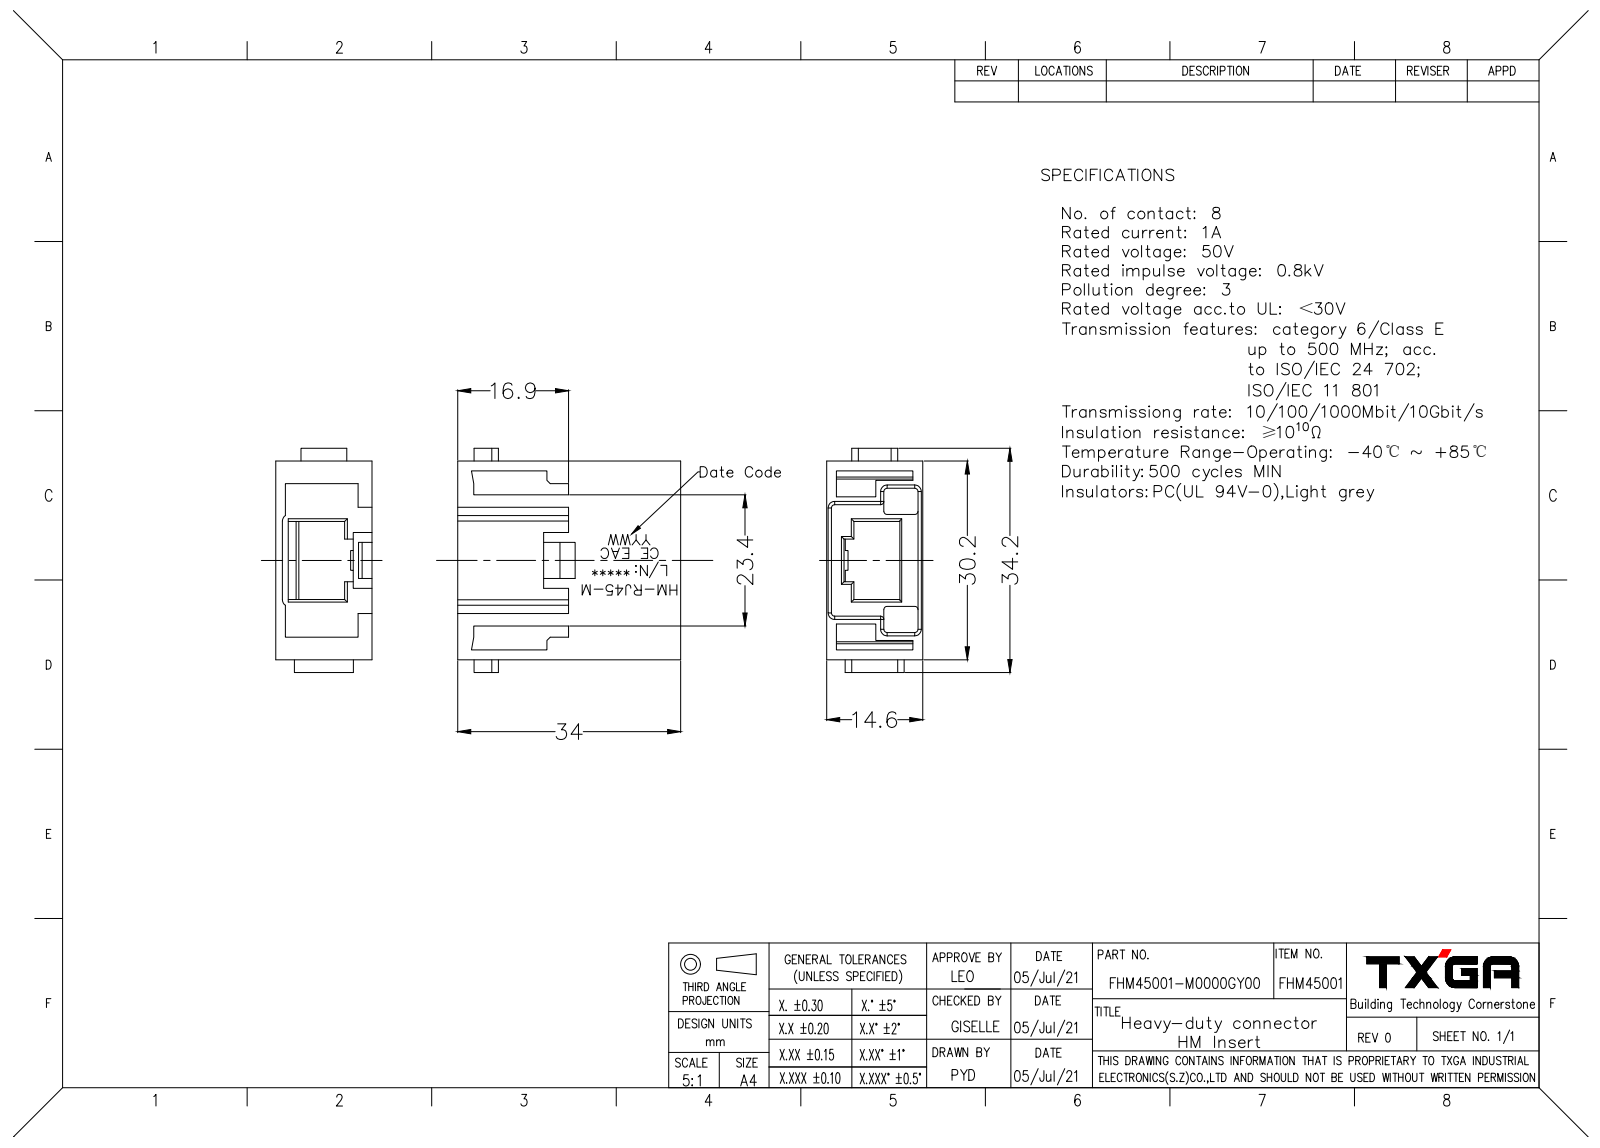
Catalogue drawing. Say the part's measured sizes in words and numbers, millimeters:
The part is named "FHM45001-M0000GY00". Its 3-D file was written by "SolidWorks 2021 (CONFIG_CONTROL_DESIGN)". It is 1 solid with 126 faces: 106 planar, 16 cylindrical and 4 other. Overall it measures 34.2 by 34 by 14.65 millimeters. Its volume is 4 515 cubic millimeters and its surface area 6 888 square millimeters. Partial cylindrical surfaces (rounded edges, fillets, slot ends): 9 of radius 0.2, 6 of radius 1. The main face-to-face distances are 14.66, 1.5, 0.61, 14.05, 30.3, 1.55, 28.8, 13.16, 0.89, 12.55.
